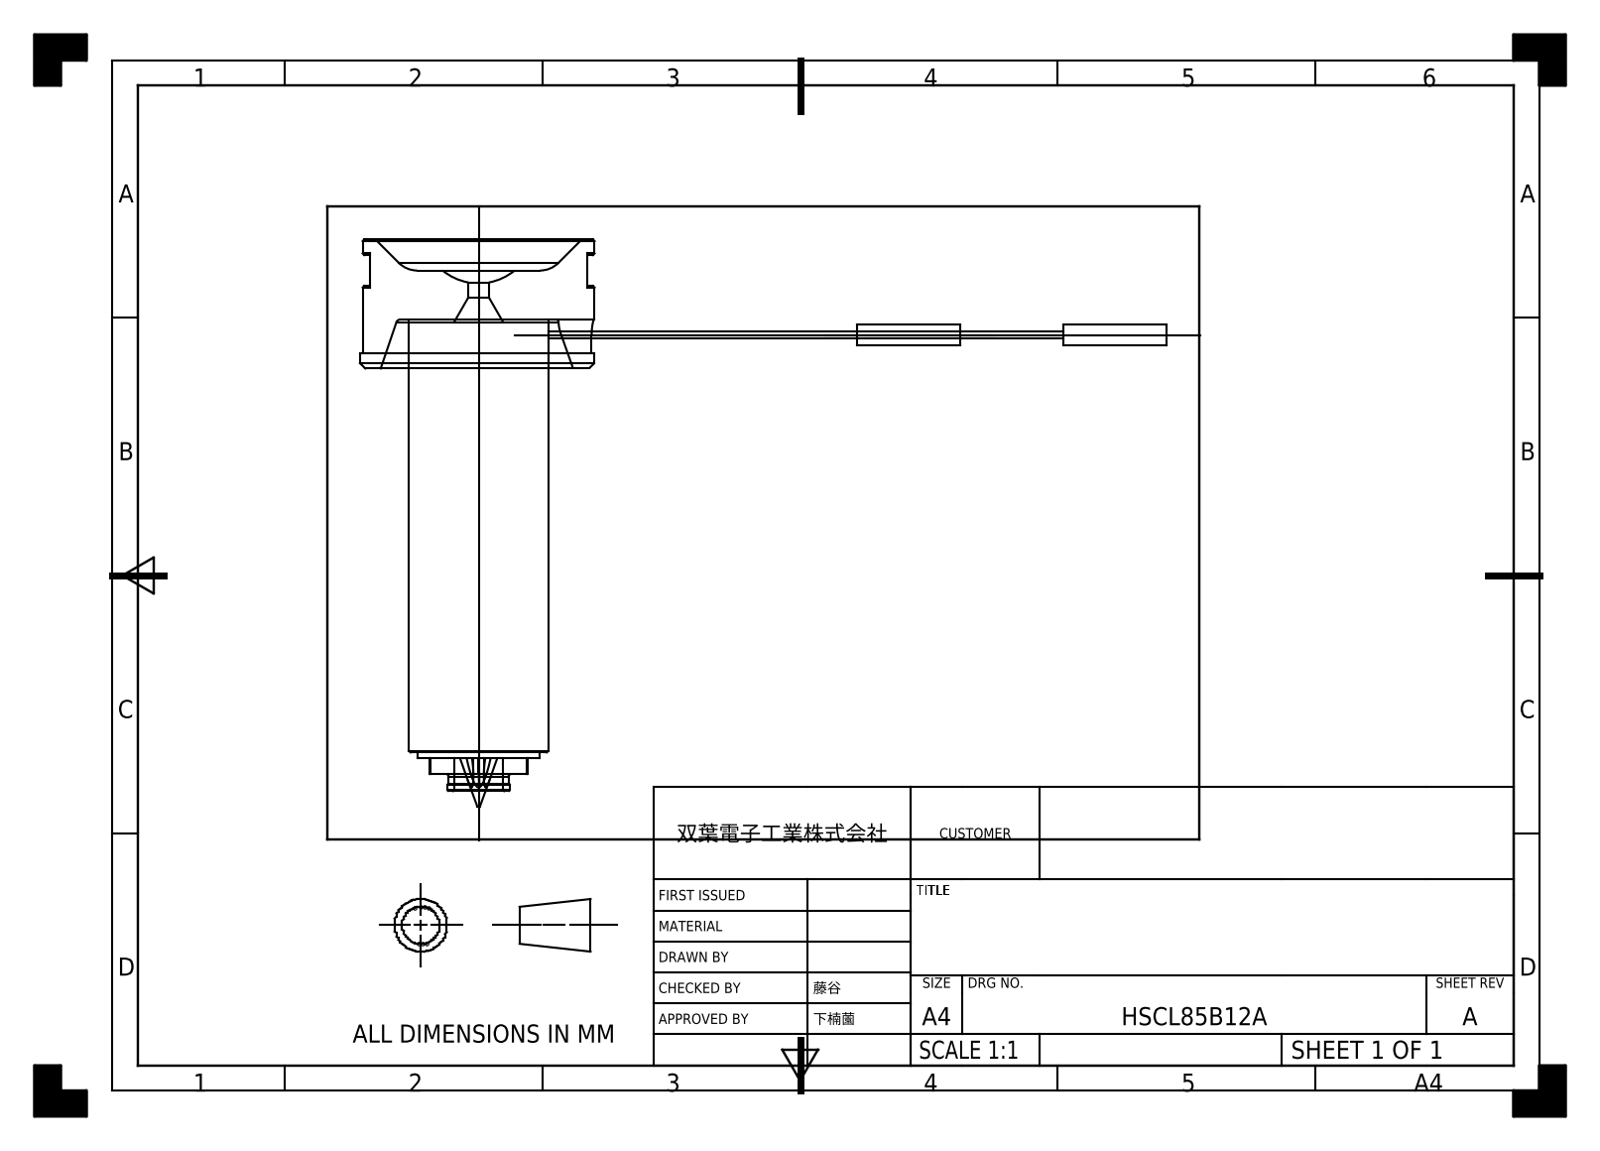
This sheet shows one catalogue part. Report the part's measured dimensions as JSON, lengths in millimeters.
{"part_name": "HSCL85B12A", "step_written_by": "SIEMENS PLM Software NX 2023 (AUTOMOTIVE_DESIGN)", "units": "millimeters", "bodies": {"solids": 5, "faces": 75, "planar": 34, "cylindrical": 23, "other": 18}, "overall_size": [156.5, 110, 46], "volume_mm3": 74529, "surface_area_mm2": 16903, "round_holes": [[4, 1], [9.5, 1]], "round_bosses_or_shafts": [[4, 2], [1.2, 2], [46, 1], [45, 1], [27, 1], [23.8, 1], [12, 1], [11.6, 1]], "partial_cylinders_radius": [[2.8, 3], [3, 2], [10.9, 1]], "face_to_face_distances": [19, 6, 9.5, 25, 85, 94.5, 103.7, 97.7, 78.7, 15.5]}
